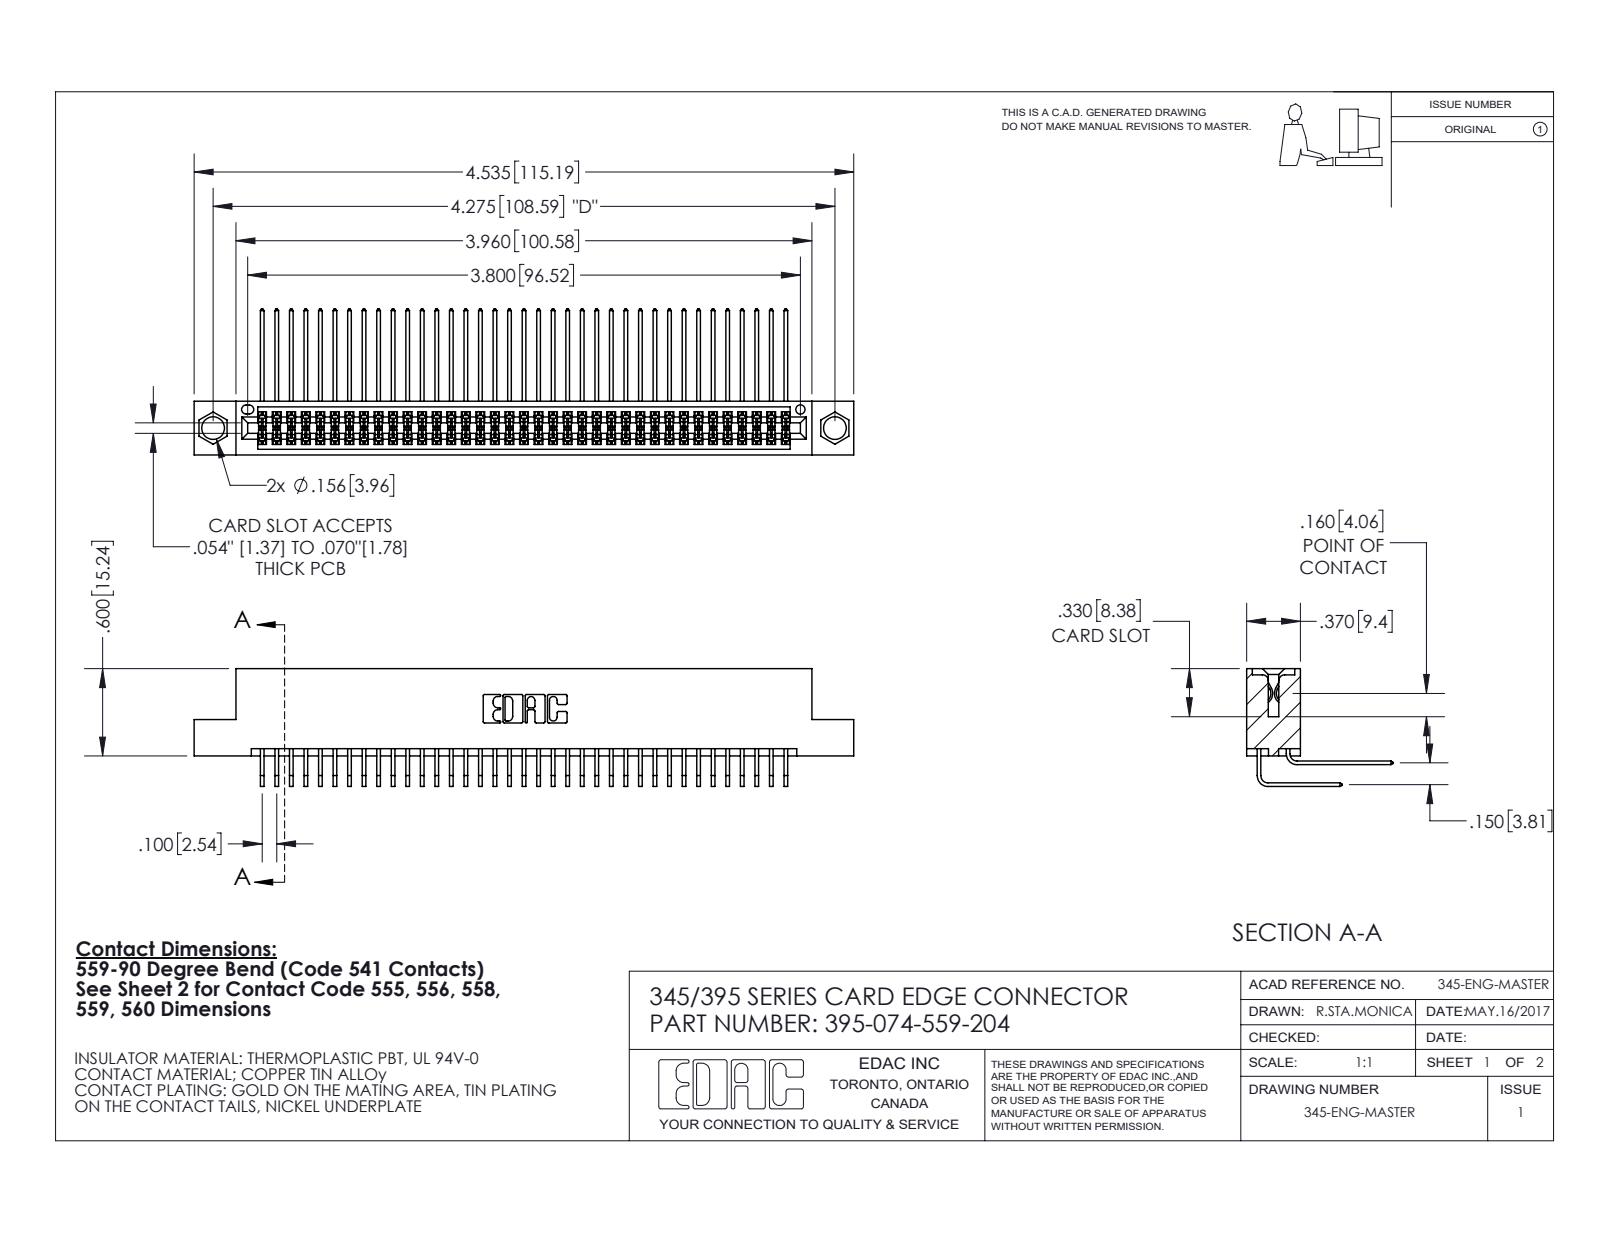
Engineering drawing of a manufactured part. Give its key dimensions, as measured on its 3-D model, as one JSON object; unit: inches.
{"part_name": "395-074-559-204; 345-292-001_559 Tail - 2; 345-292-001_558 559 Tail - 1; 345 Part_Flush Mounting Lugs - 0.156 Dia-TI", "step_written_by": "SolidWorks 2020 (CONFIG_CONTROL_DESIGN)", "units": "inches", "bodies": {"solids": 75, "faces": 3988, "planar": 2684, "cylindrical": 1304, "other": 0}, "overall_size": [4.535, 1.005, 0.809], "volume_in3": 0.7, "surface_area_in2": 29, "round_holes": [[0.156, 2], [0.064, 1]], "partial_cylinders_radius": [[0.006, 111], [0.01, 22], [0.007, 6], [0.031, 6], [0.026, 3], [0.014, 2], [0.019, 2], [0.022, 2]], "face_to_face_distances": [0.072, 0.298, 0.2, 0.37, 0.098, 0.272, 0.025, 0.225, 0.175, 0.15], "hole_center_spacings": [0.27, 4.039, 4.275]}
